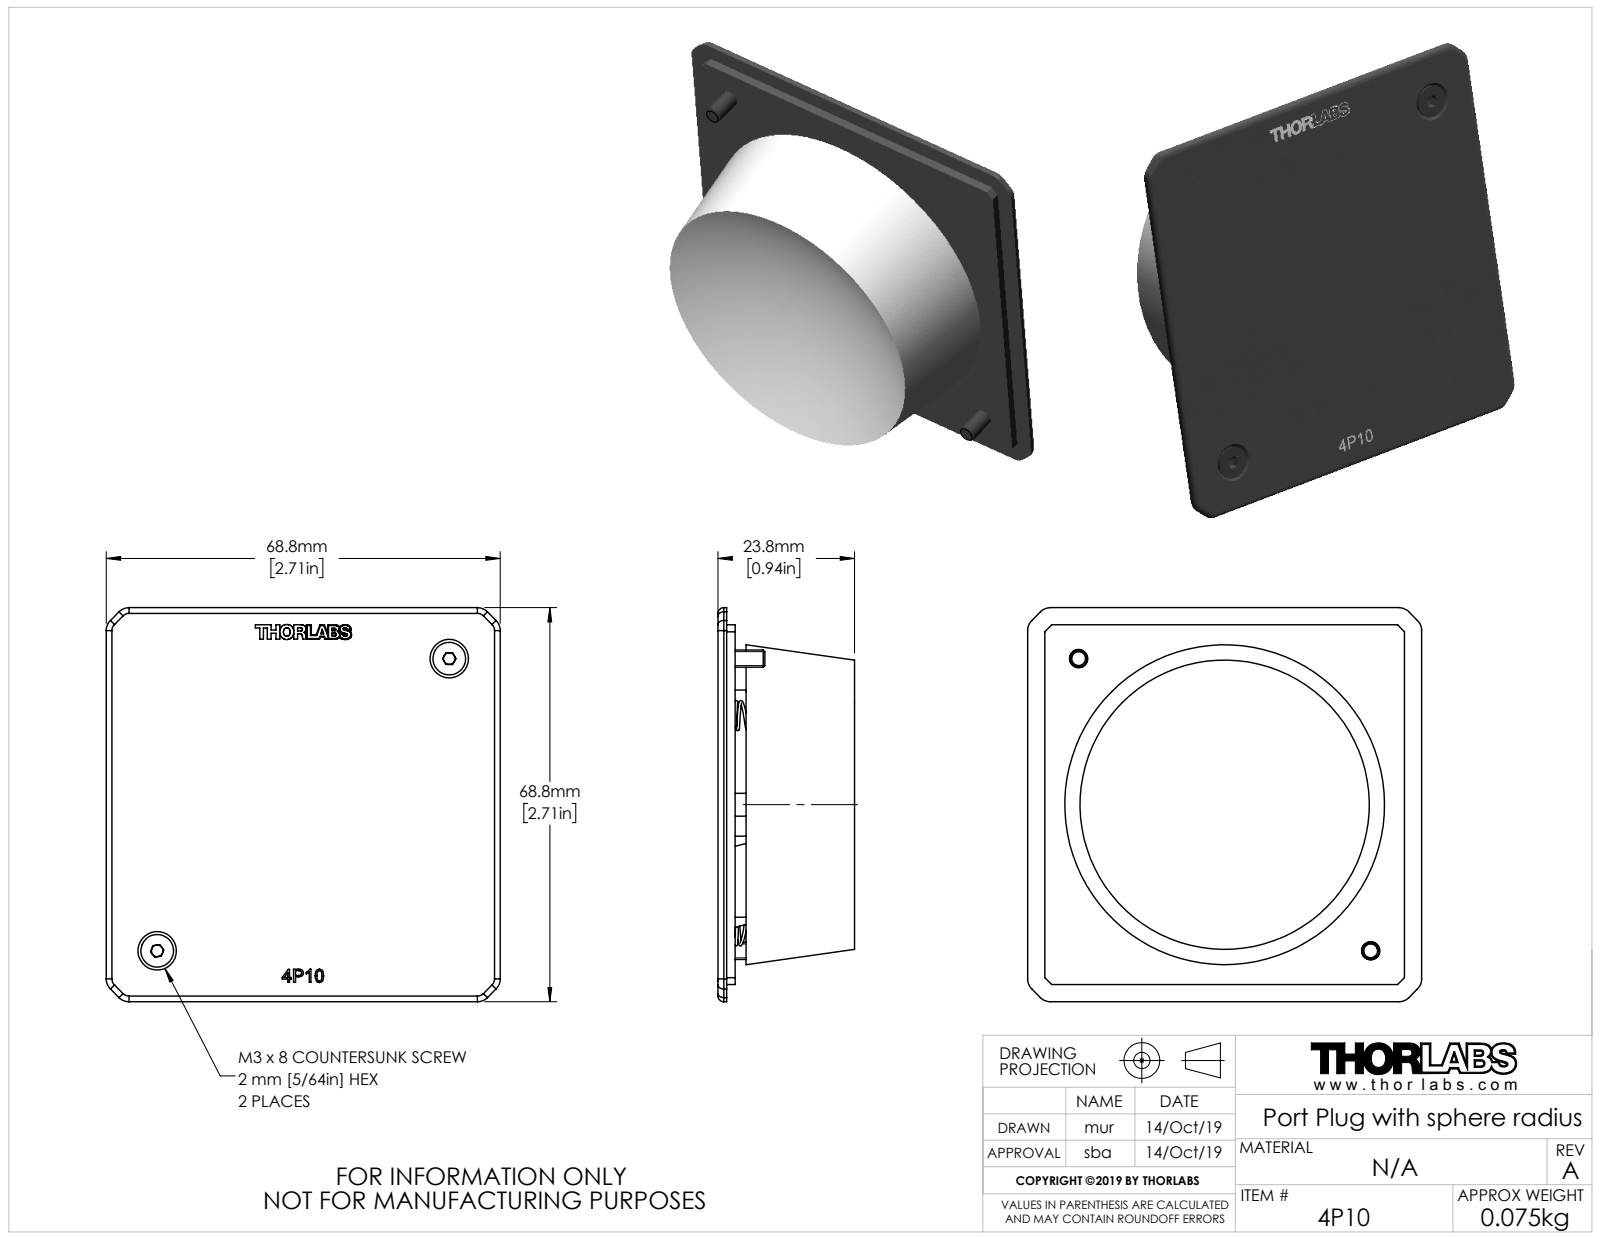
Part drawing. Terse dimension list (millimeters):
name: 19.11.04_4P10_Port Plug with adapted sphere radius WEB
written by: SolidWorks 2018 (AUTOMOTIVE_DESIGN)
unit: mm
bodies: 10 solids, 779 faces (607 planar, 68 cylindrical, 104 other)
size: 68.8 × 68.8 × 23.84
volume: 47 270 mm³; area: 20 550 mm²
holes: 3× ⌀4, 3× ⌀4.5, 3× ⌀5.5, 3× ⌀6.5, 2× ⌀3.2
bosses: 3× ⌀5.5, 2× ⌀5.7, 2× ⌀3
rounds: 8× R1, 8× R2.5, 4× R1.5
face distances: 3, 4.9, 1.9, 1.5, 3.4, 4.4, 2.5, 5.9, 7.4, 20
hole spacings: 16.84, 25.74, 31.11, 40.66, 53.91, 14.06, 44, 58.07
